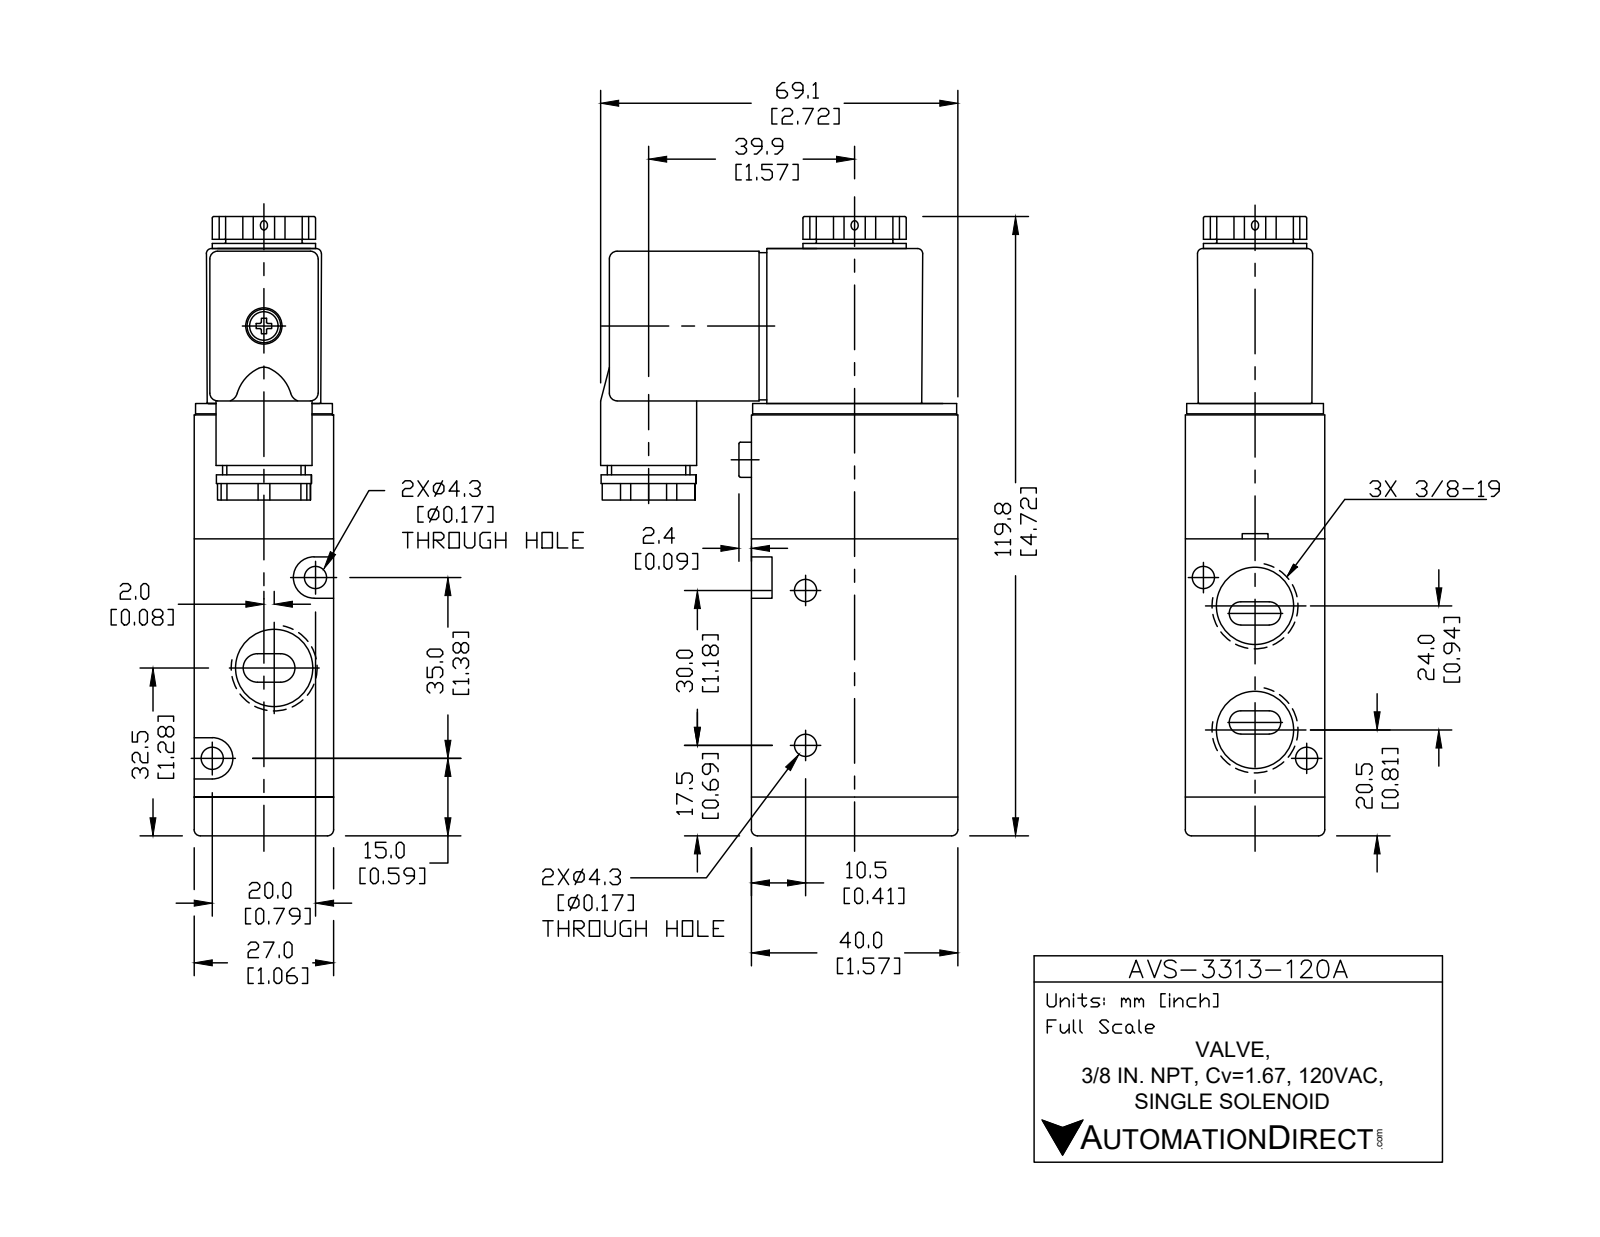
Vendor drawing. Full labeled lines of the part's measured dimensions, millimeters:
Part name (STEP PRODUCT): AVS-3313-120A
STEP written by: SolidWorks 2015 (CONFIG_CONTROL_DESIGN)
Units: millimetres
Bodies: 4 solids, 156 faces (81 planar, 53 cylindrical, 22 other)
Overall size (bounding box): 119.9 × 69.1 × 27
Volume: 124 534 mm³ · Surface area: 29 364 mm²
Round holes (diameter × count): ⌀4.3 ×4, ⌀14.27 ×3, ⌀9.3 ×1
Round bosses / shafts (diameter × count): ⌀20 ×1, ⌀18.6 ×1, ⌀18.4 ×1, ⌀16 ×1, ⌀14.8 ×1, ⌀6.8 ×1
Partial cylindrical surfaces — rounded edges, fillets, slot ends (radius × count): R0.5 ×11, R1 ×10, R4 ×2
Main face-to-face distances: 50, 27, 3, 24, 7.5, 57.5, 21, 2.26, 2.27, 40
Hole centre spacings: 11.41, 12.17, 31.15, 19.24, 21.22, 24, 30, 40.31
